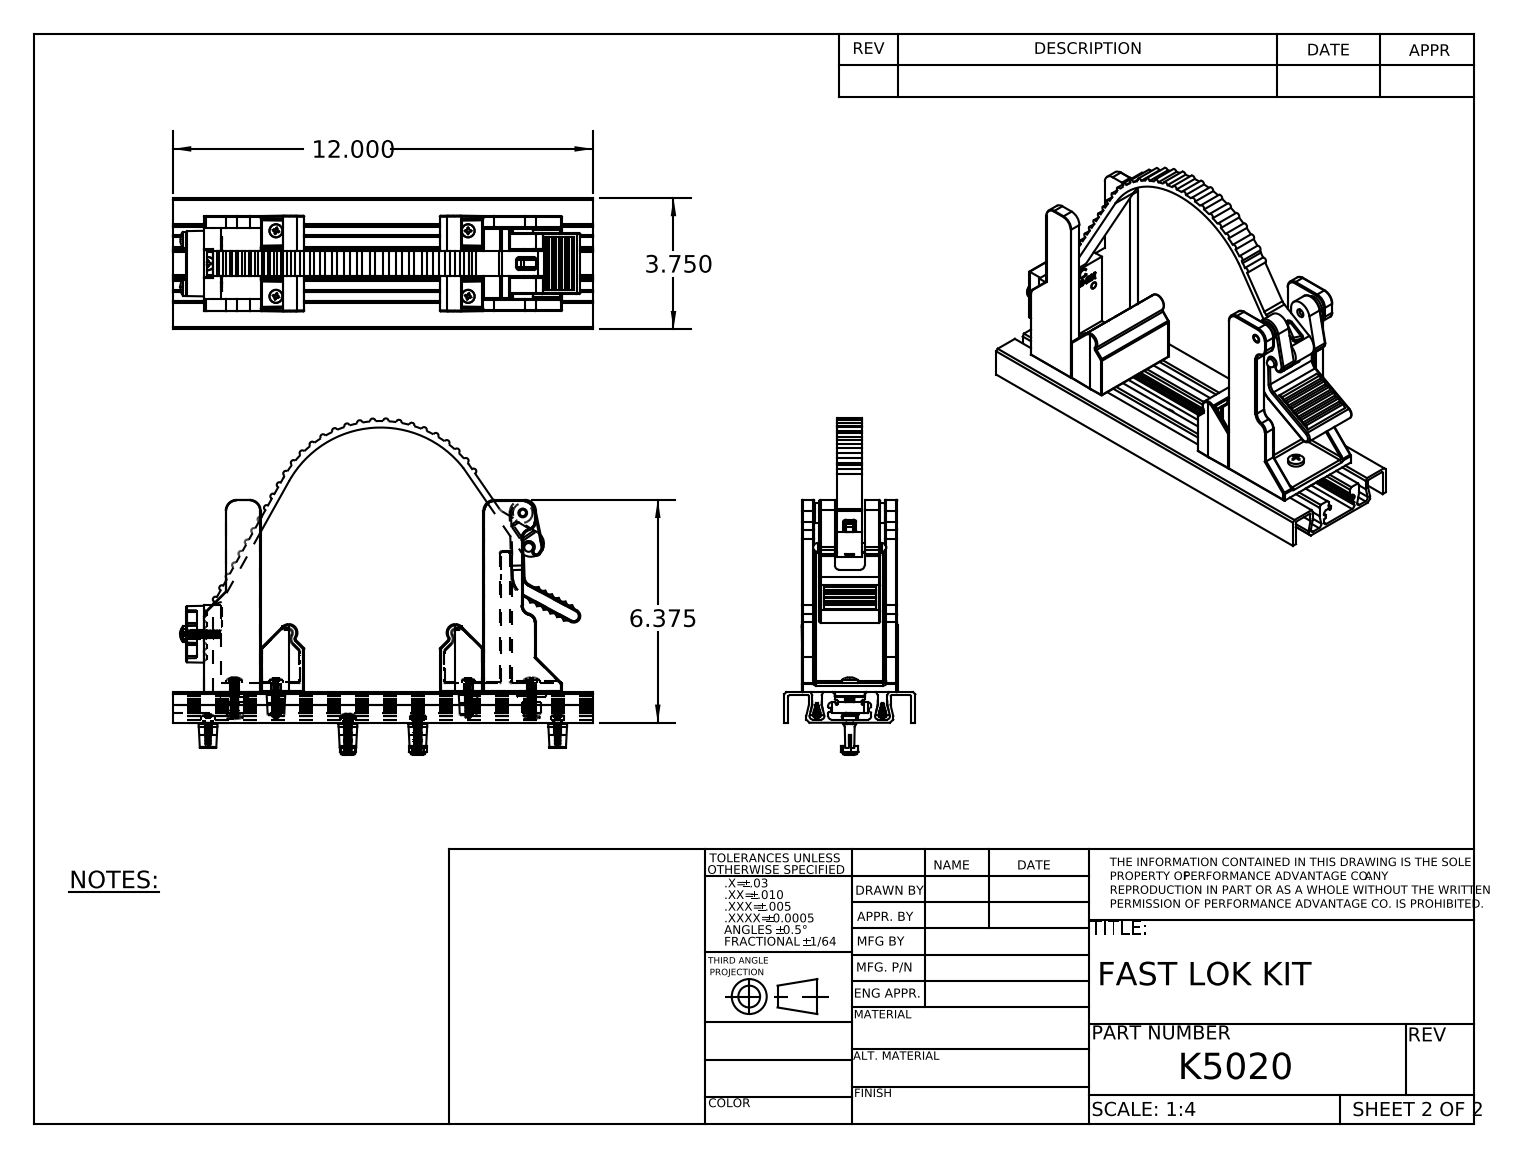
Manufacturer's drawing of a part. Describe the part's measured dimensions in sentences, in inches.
The part is named "K5020; 1020-901; 1020-204; 1020-203 (+8 more)". Its 3-D file was written by "SolidWorks 2010 (CONFIG_CONTROL_DESIGN)". It is 45 solids with 4177 faces: 1368 planar, 824 cylindrical and 1985 other. Overall it measures 12 by 9.619 by 3.75 inches. Its volume is 41.09 cubic inches and its surface area 509 square inches. Round holes: 12 of diameter 0.201, 4 of diameter 0.266, 3 of diameter 0.25, 2 of diameter 0.26, 2 of diameter 0.269, 2 of diameter 0.281. Round bosses or shafts: 8 of diameter 0.375, 8 of diameter 0.187, 6 of diameter 0.46, 6 of diameter 0.25, 2 of diameter 0.404, 1 of diameter 0.563. Partial cylindrical surfaces (rounded edges, fillets, slot ends): 150 of radius 0.031, 29 of radius 0.078, 21 of radius 0.062, 16 of radius 0.016, 12 of radius 0.04, 10 of radius 0.25, 9 of radius 0.029, 8 of radius 0.02. The main face-to-face distances are 0.876, 0.343, 2.376, 0.342, 0.093, 0.782, 0.393, 3.112, 0.25, 0.393. The hole center spacings are 0.937, 5.574, 5.495, 1.513, 1.716, 1.875, 2.041, 2.157.
